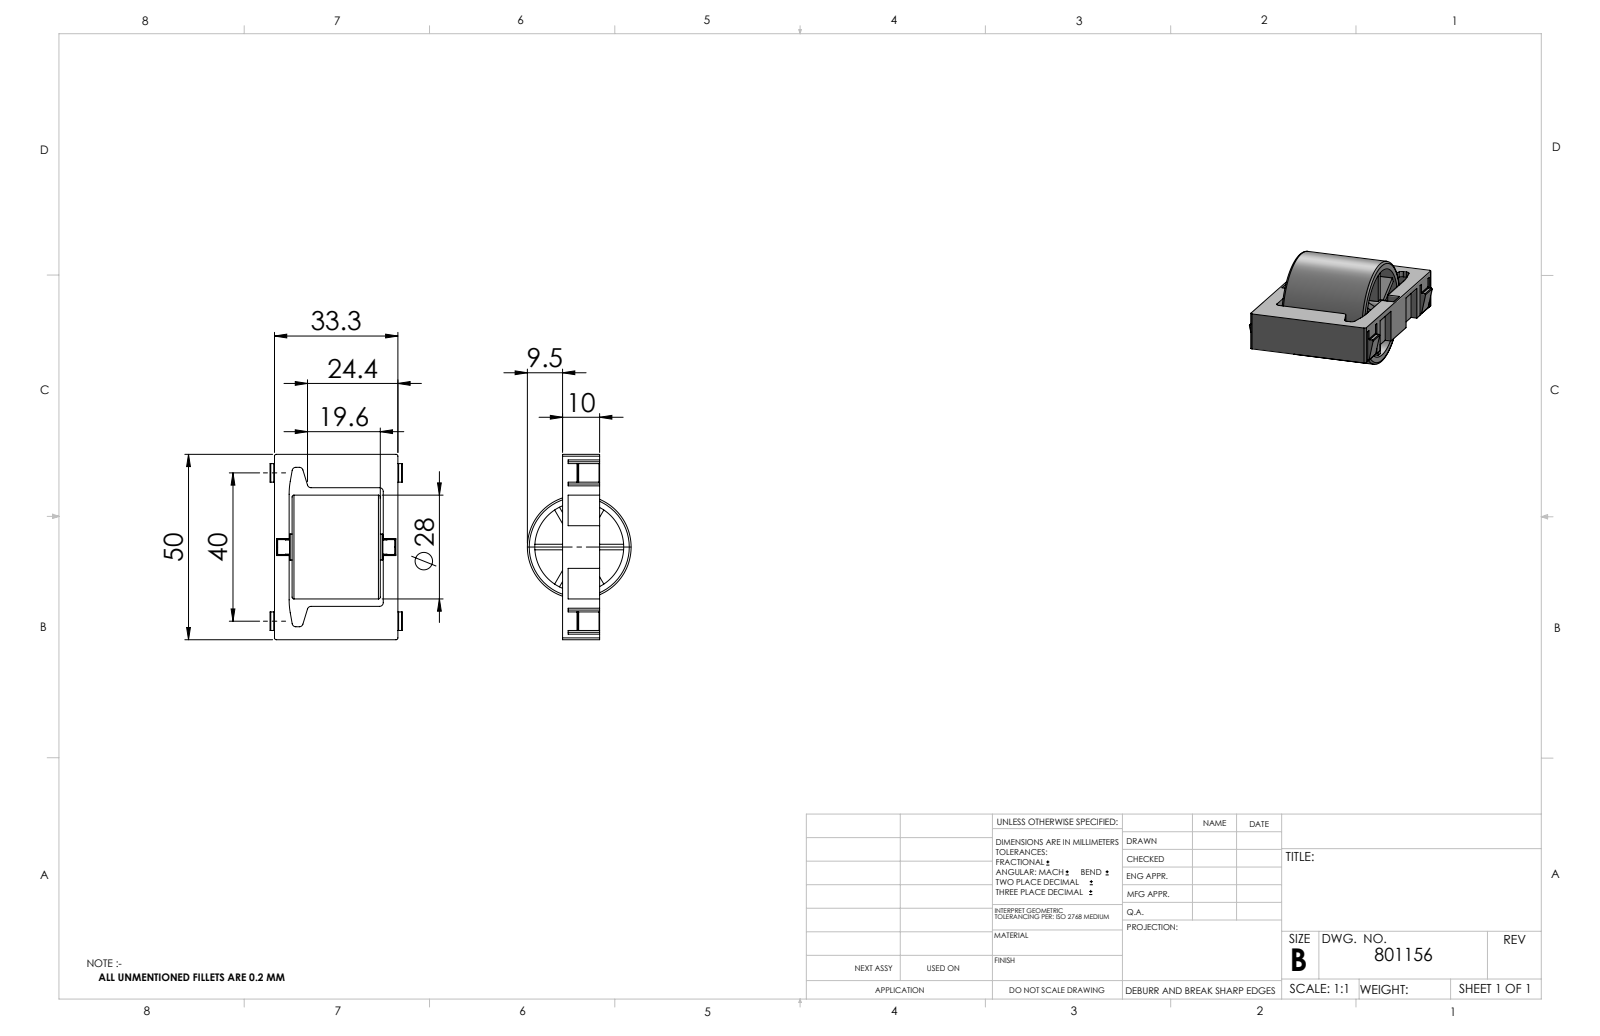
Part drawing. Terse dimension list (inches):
name: 062AER2874.50-1; 801156_c_1; 062AER2874.50-3; 062AER2874.50-2
written by: SolidWorks 2014 (CONFIG_CONTROL_DESIGN)
unit: in
bodies: 3 solids, 238 faces (152 planar, 74 cylindrical, 12 other)
size: 1.969 × 1.406 × 1.102
volume: 0.697 in³; area: 21.04 in²
holes: 1× ⌀0.165, 1× ⌀0.945
bosses: 1× ⌀1.102, 1× ⌀0.276, 1× ⌀0.157
rounds: 16× R0.02, 12× R0.008, 8× R0.039, 2× R0.006, 2× R0.787, 1× R0.081
face distances: 0.059, 0.484, 0.031, 0.955, 0.516, 1.014, 1.156, 0.335, 0.098, 0.856
